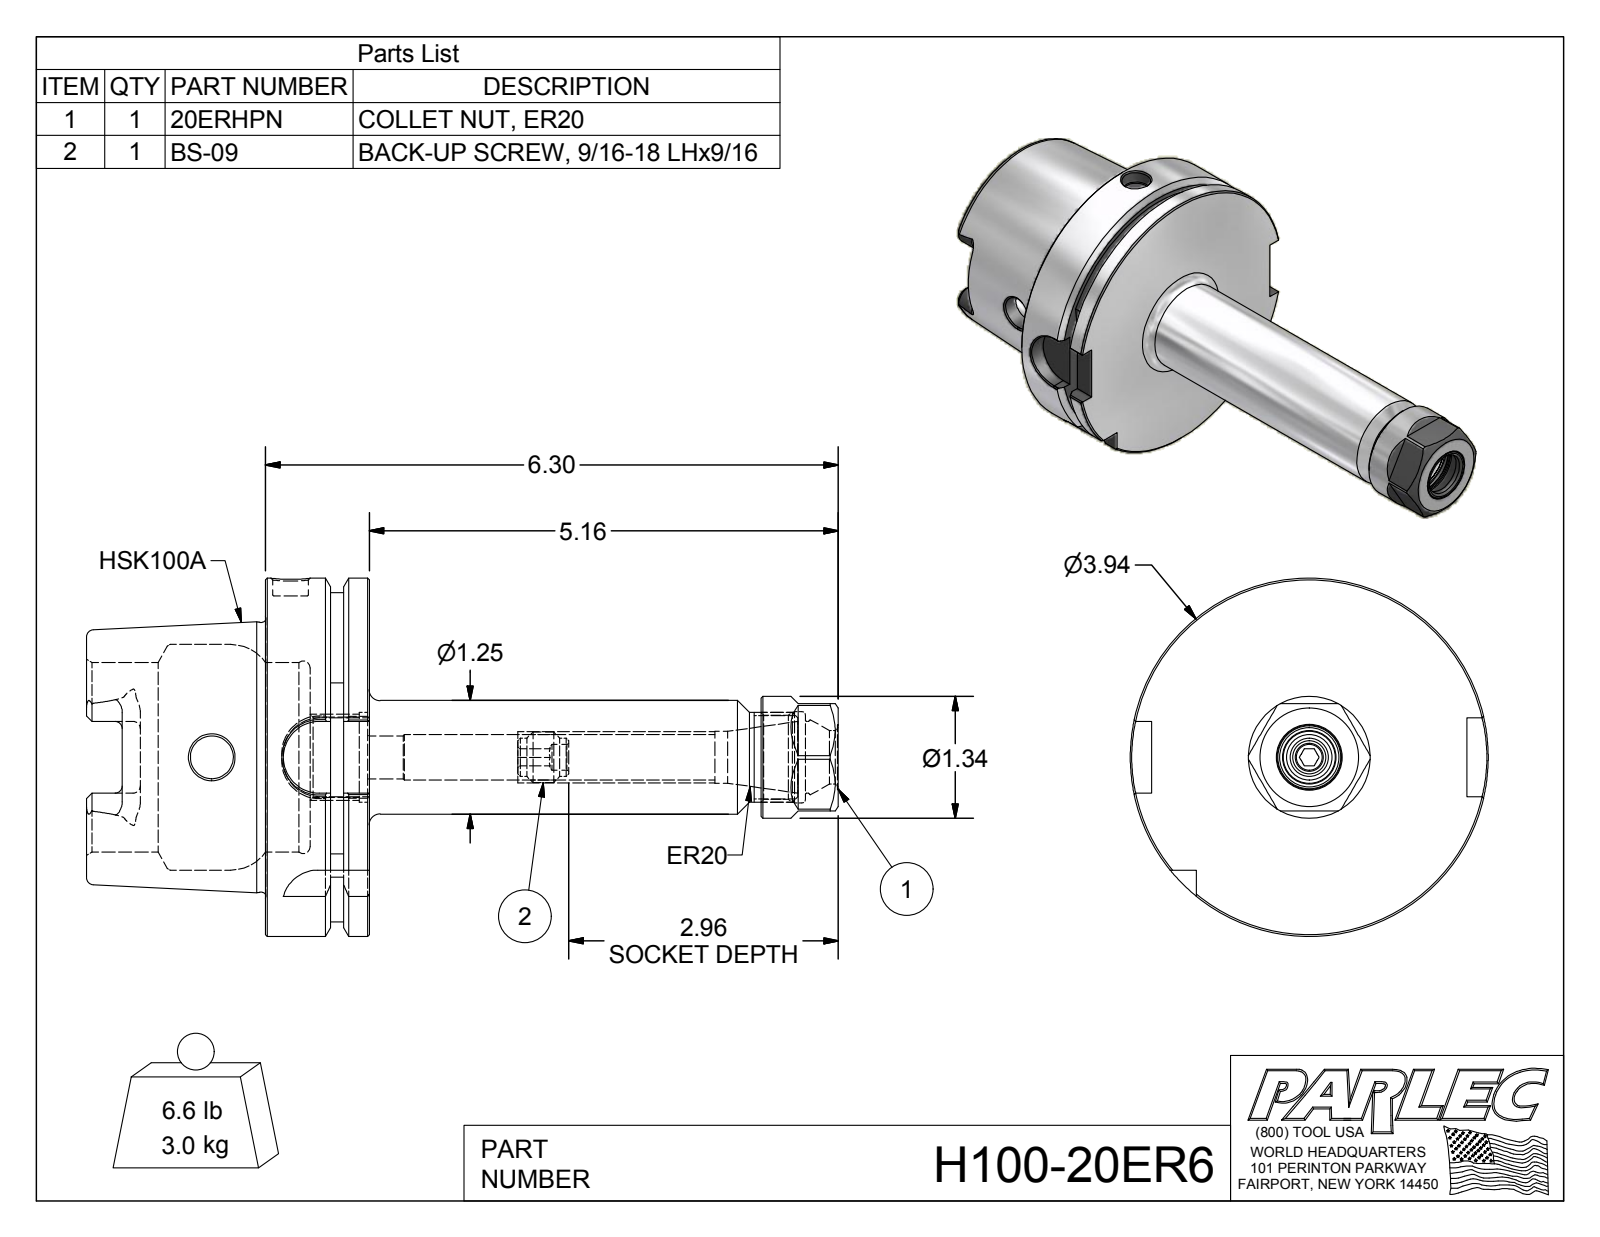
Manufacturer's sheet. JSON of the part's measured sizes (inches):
{"part_name": "H100-20ER6; H100-20ER6-1; BS-09; 20ERHPN", "step_written_by": "Autodesk Inventor 2012 (AUTOMOTIVE_DESIGN)", "units": "inches", "bodies": {"solids": 3, "faces": 187, "planar": 74, "cylindrical": 45, "other": 68}, "overall_size": [8.269, 3.937, 3.937], "volume_in3": 20.62, "surface_area_in2": 111.4, "round_holes": [[0.472, 2], [0.281, 1], [0.394, 1], [0.472, 1], [0.502, 1], [0.57, 1], [0.587, 1], [0.79, 1], [0.881, 1], [0.926, 1], [0.985, 1], [1.005, 1]], "round_bosses_or_shafts": [[3.937, 1], [2.967, 1], [1.34, 1], [1.25, 1], [0.984, 1], [0.555, 1], [0.422, 1]], "partial_cylinders_radius": [[0.079, 6], [0.192, 4], [0.394, 4], [1.811, 1]], "face_to_face_distances": [1.142, 0.492, 0.65, 1.969, 2.461, 3.11, 2.83, 0.861, 0.369, 0.28]}
